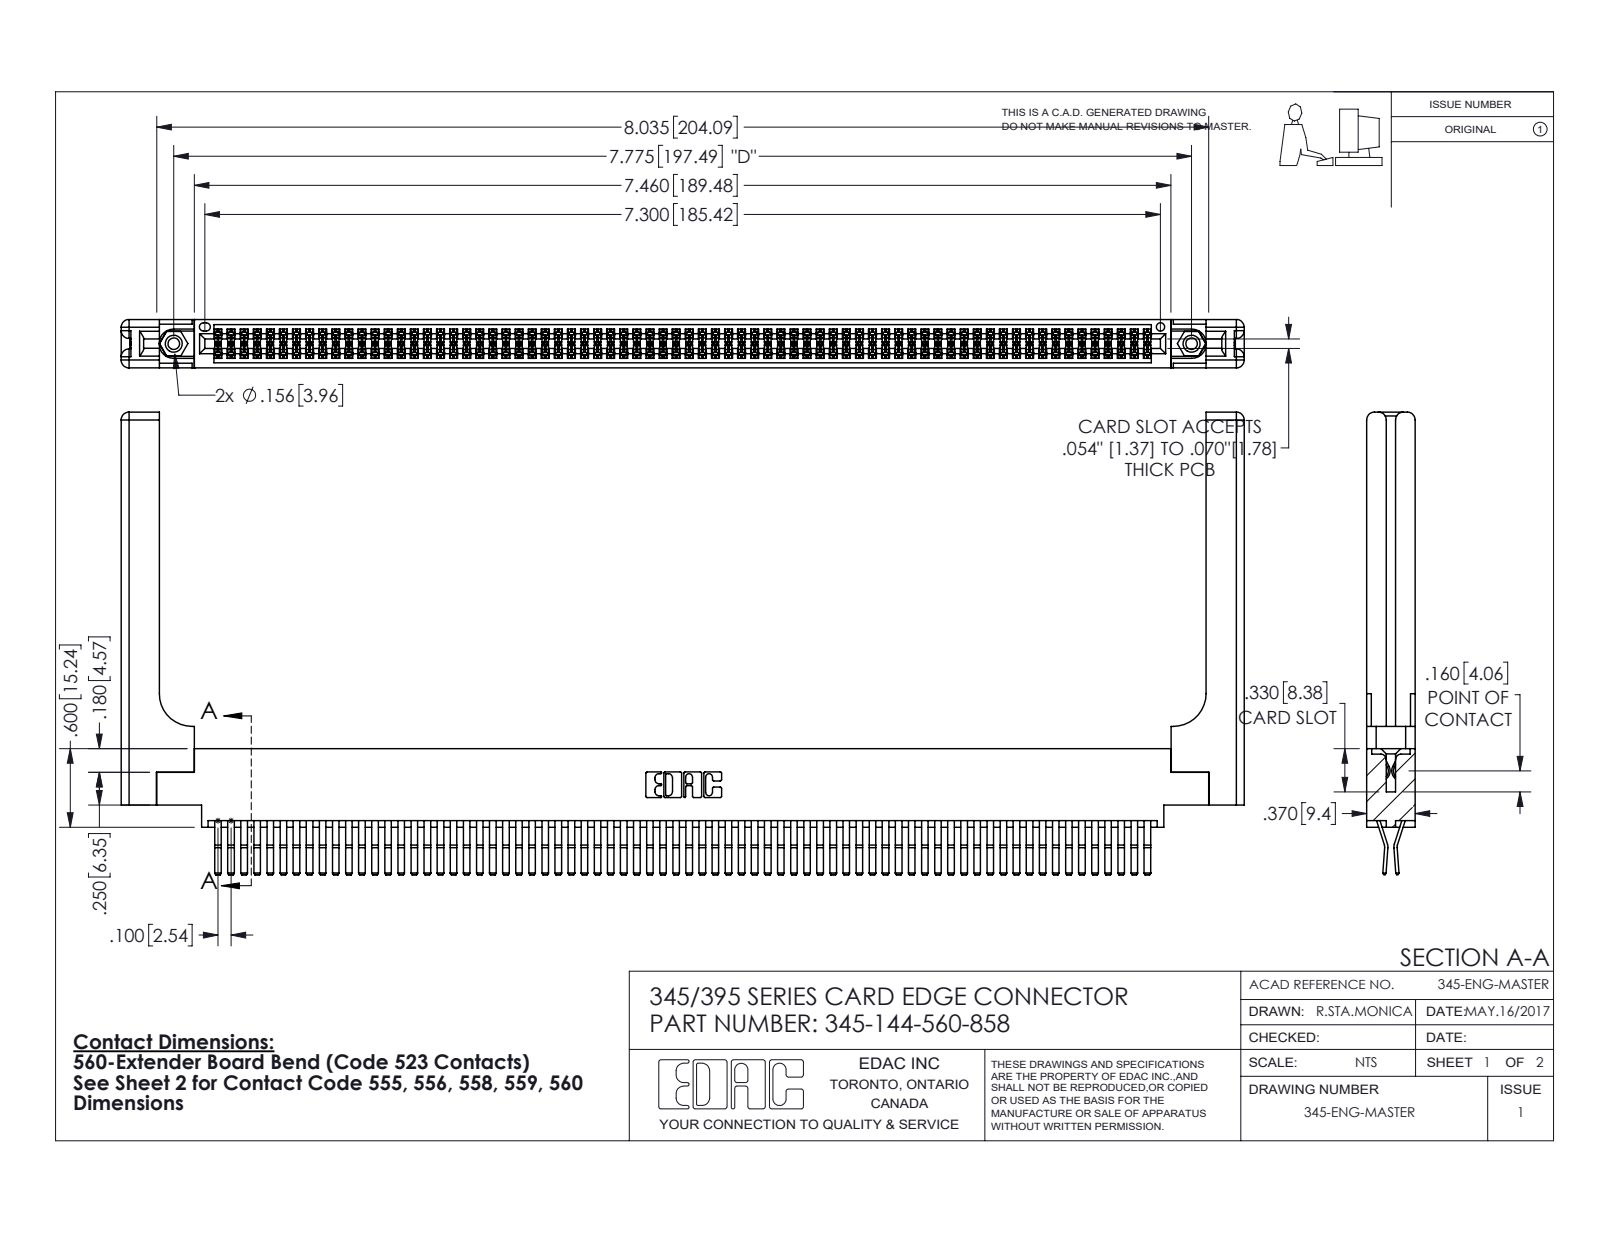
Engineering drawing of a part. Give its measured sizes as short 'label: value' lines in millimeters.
name: 345-220-058_345-220-058; 345-292-001_560 Tail; 345 Part_0.170 Offset - 0.156 Dia-TH; 345-250-001_345-250-001-102 (+1 more)
written by: SolidWorks 2016 (CONFIG_CONTROL_DESIGN)
unit: mm
bodies: 149 solids, 7874 faces (4984 planar, 2830 cylindrical, 60 other)
size: 217.9 × 89.7 × 9.4
volume: 30 760 mm³; area: 41 140 mm²
holes: 2× ⌀2.3, 2× ⌀3.2, 2× ⌀4, 1× ⌀1.6
bosses: 2× ⌀3.9
rounds: 217× R0.2, 22× R0.3, 16× R1.5, 6× R0.2, 6× R0.8, 3× R0.7, 2× R0.3, 2× R0.4
face distances: 1.8, 7.6, 0.6, 9.4, 2.5, 6.9, 5.1, 5.7, 4.4, 3.8
hole spacings: 6.9, 191.5, 197.5
